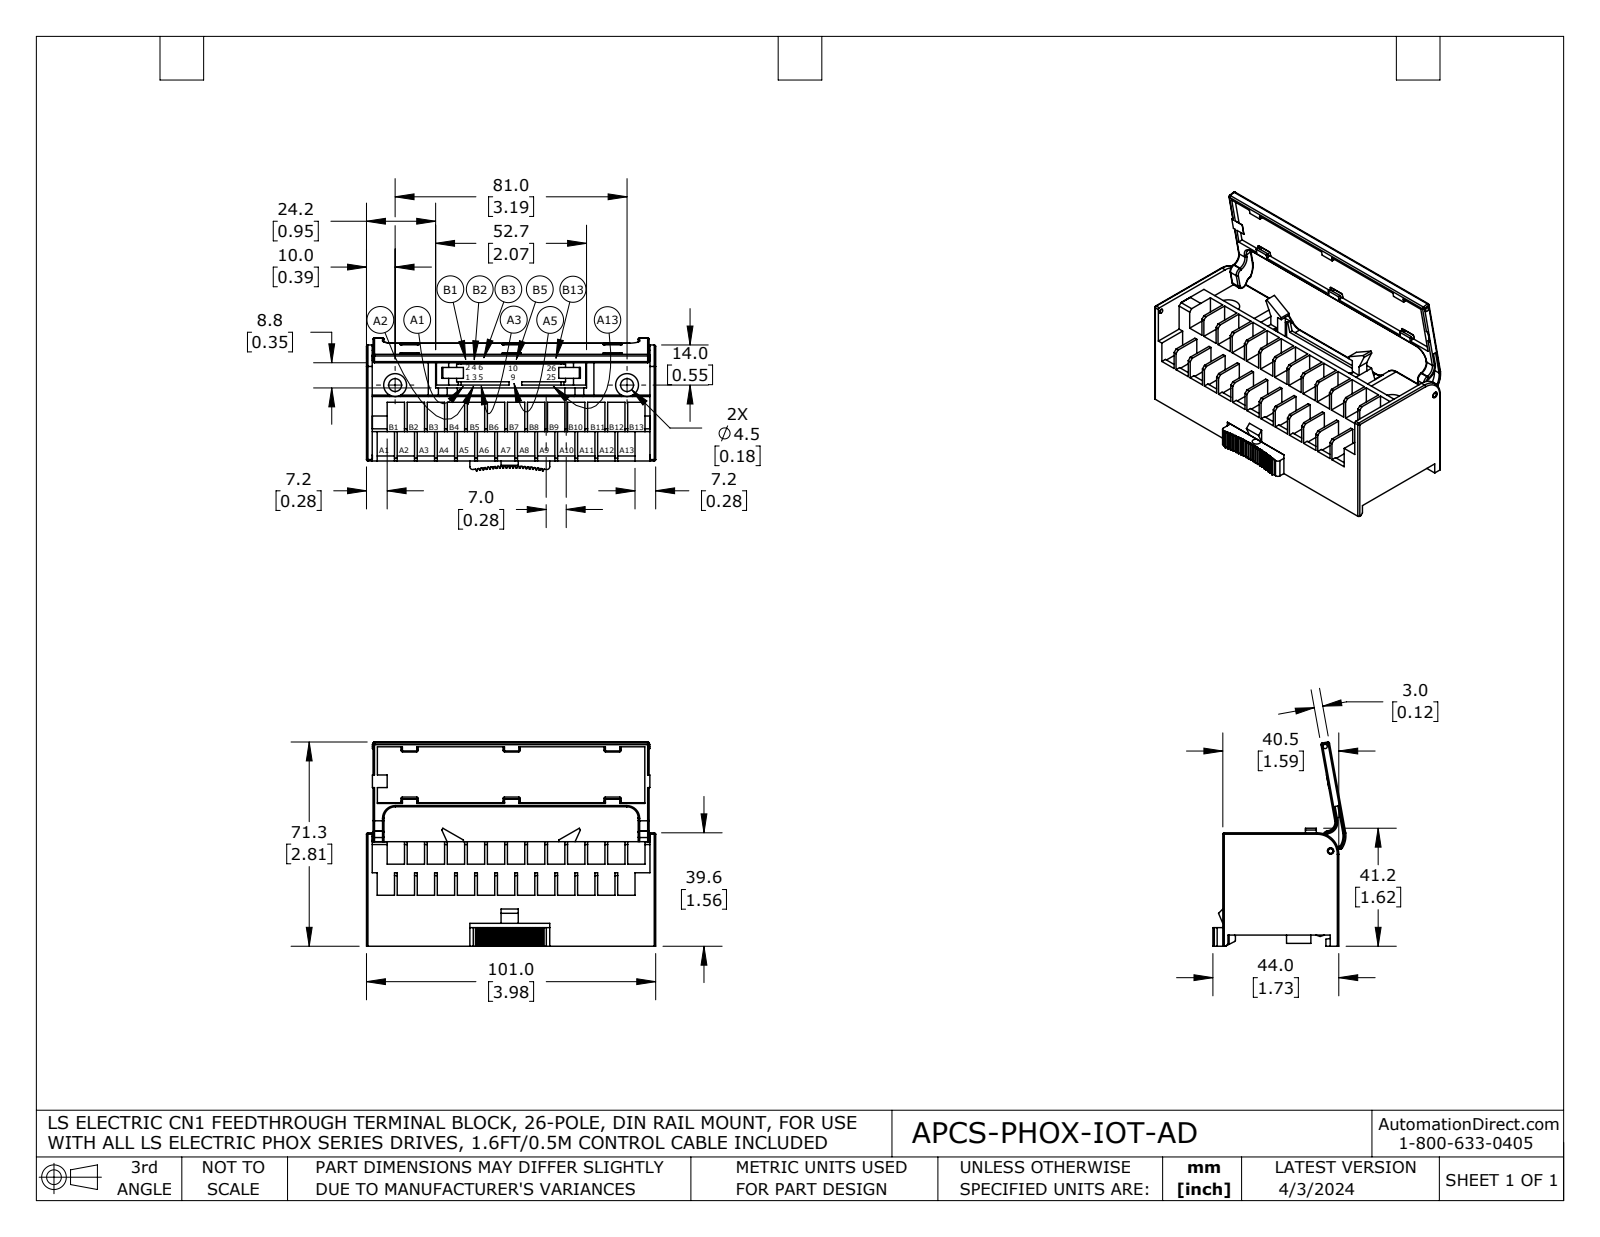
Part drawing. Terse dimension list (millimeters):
name: APCS-PHOX-IOT-AD
written by: SolidWorks 2021 (AUTOMOTIVE_DESIGN)
unit: mm
bodies: 2 solids, 694 faces (458 planar, 175 cylindrical, 61 other)
size: 101 × 44 × 41.2
volume: 99 720 mm³; area: 34 600 mm²
holes: 2× ⌀4.5, 2× ⌀8, 1× ⌀2.2, 1× ⌀3
bosses: 2× ⌀8.5, 1× ⌀2, 1× ⌀1.5
rounds: 67× R0.5, 5× R4, 4× R1, 4× R2, 4× R5, 2× R0.3, 2× R0.4, 2× R5.5
face distances: 1.5, 10.3, 40.5, 101, 14, 2, 24.7, 40.3, 3, 30.3
hole spacings: 47.8, 48.6, 81
